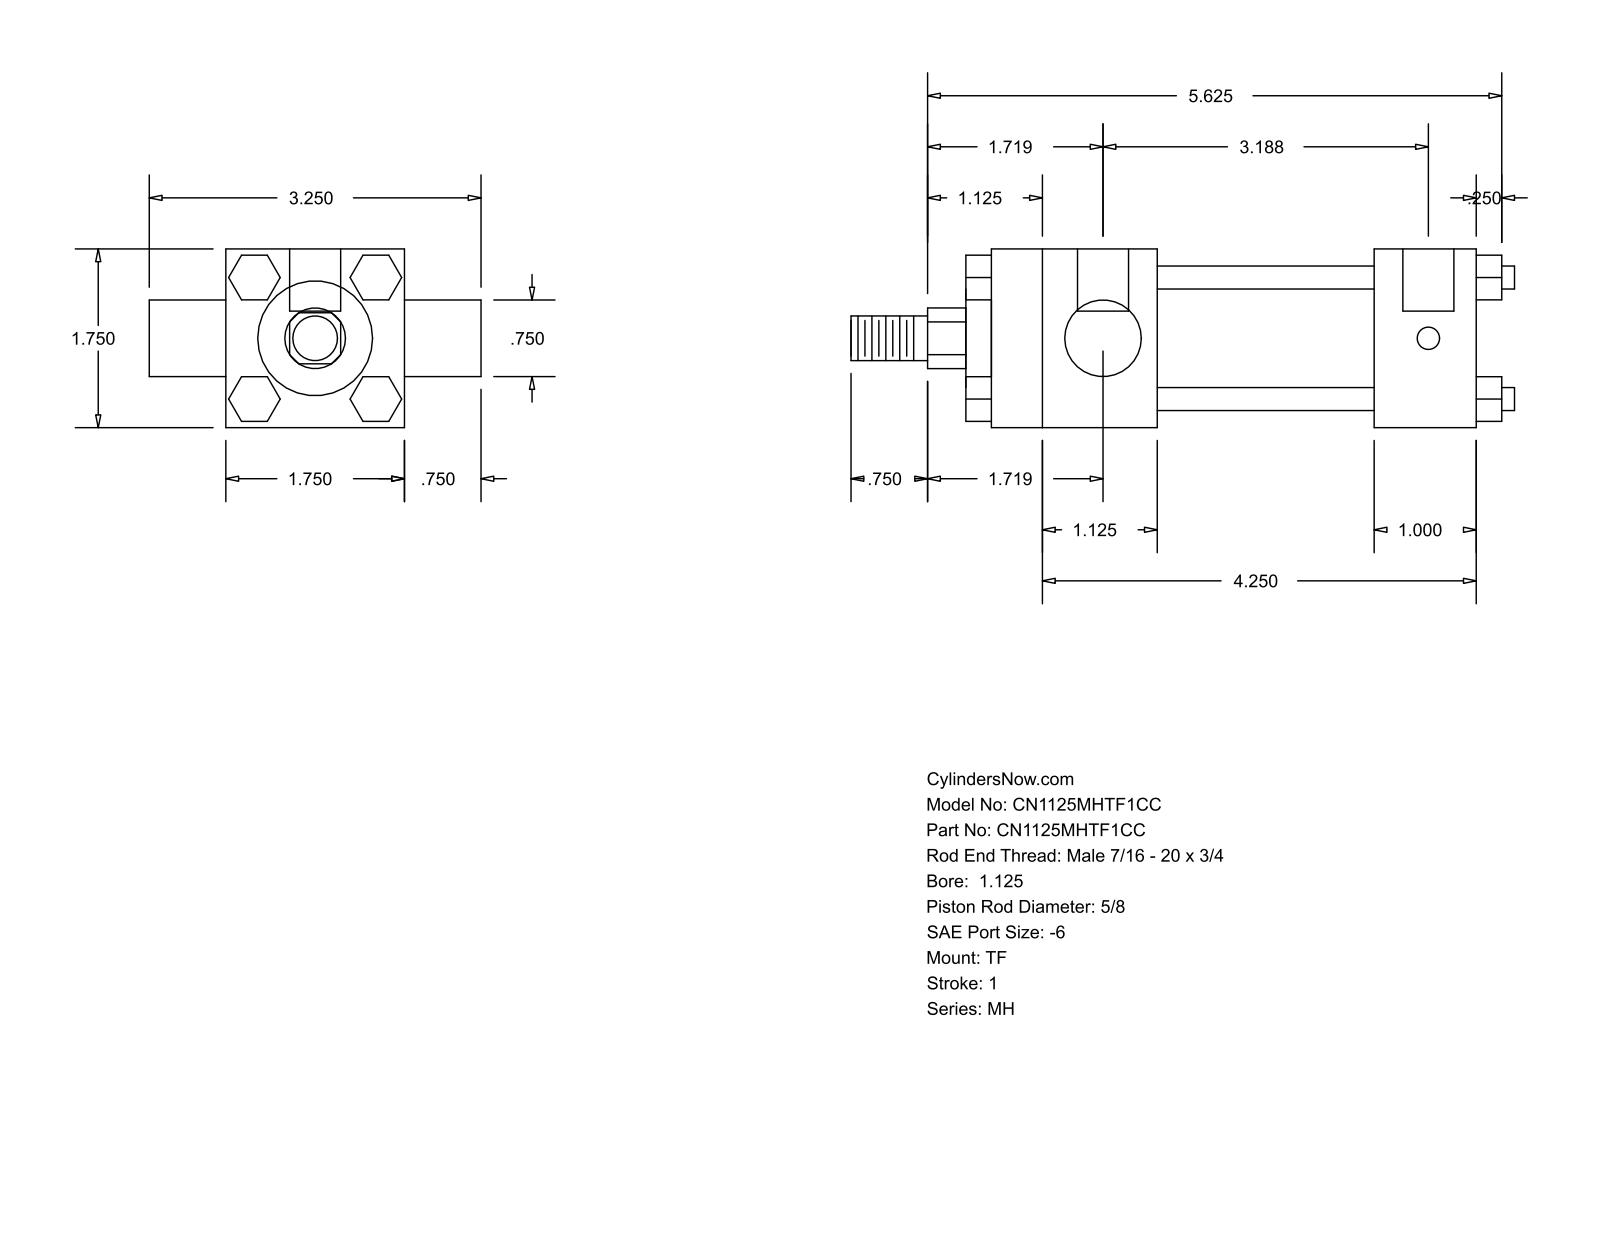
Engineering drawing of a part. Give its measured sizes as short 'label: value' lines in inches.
name: MH_TF__0112_0.625
written by: GSSL Pune (CONFIG_CONTROL_DESIGN)
unit: in
bodies: 0 solids, 120 faces (92 planar, 28 cylindrical, 0 other)
size: 6.5 × 3.25 × 1.75
holes: 3× ⌀0.219, 2× ⌀0.5
bosses: 4× ⌀0.225, 1× ⌀1.375, 1× ⌀1.125, 1× ⌀0.75, 1× ⌀0.625, 1× ⌀0.437
rounds: 1× R0.297
face distances: 1.75, 0.25, 5, 0.437, 2.125, 3.125, 1, 1.625, 3.75, 4.75
hole spacings: 0.125, 3.063, 3.187
